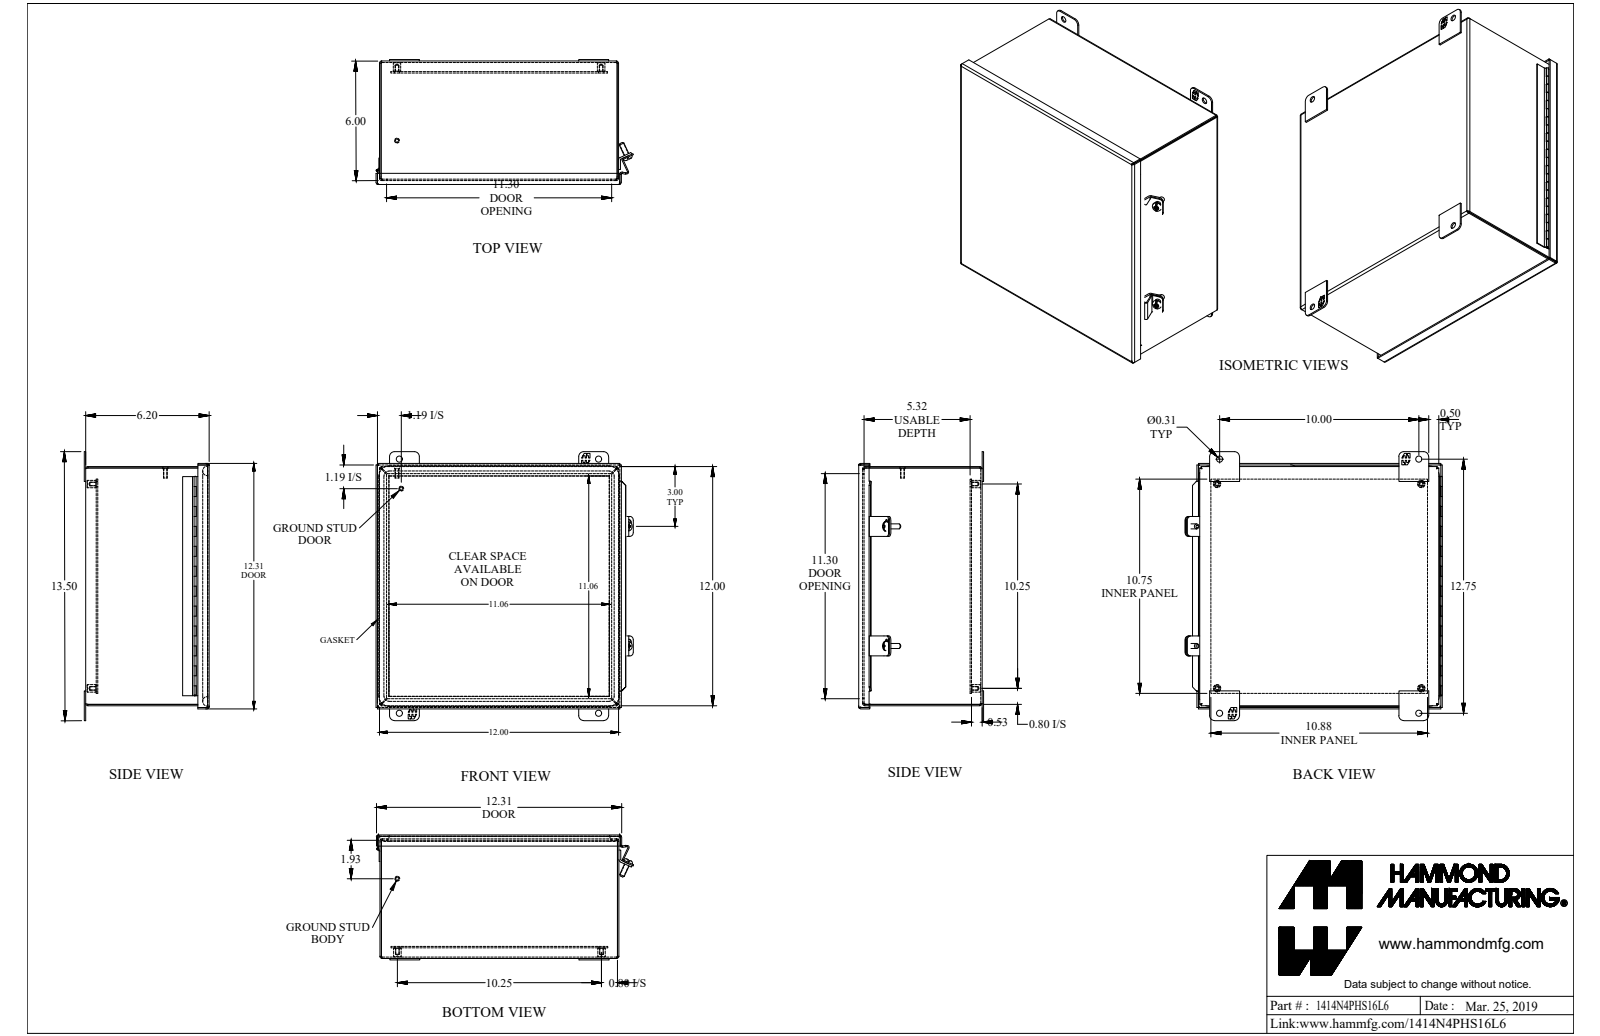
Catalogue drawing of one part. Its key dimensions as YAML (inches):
part_name: "1414N4PHS16L6"
step_written_by: "SolidWorks 2018 (AUTOMOTIVE_DESIGN)"
units: inches
bodies: {solids: 21, faces: 705, planar: 459, cylindrical: 188, other: 58}
overall_size: [13.5, 12.903, 6.269]
volume: 60.37
surface_area: 1649
round_holes:
  - {diameter: 0.156, count: 4}
  - {diameter: 0.265, count: 4}
  - {diameter: 0.313, count: 4}
  - {diameter: 0.213, count: 2}
  - {diameter: 0.05, count: 1}
round_bosses_or_shafts:
  - {diameter: 0.375, count: 4}
  - {diameter: 0.25, count: 4}
  - {diameter: 0.48, count: 2}
  - {diameter: 0.19, count: 2}
  - {diameter: 0.1, count: 1}
  - {diameter: 0.045, count: 1}
partial_cylinders:
  - {radius: 0.25, count: 24}
  - {radius: 0.036, count: 8}
  - {radius: 0.108, count: 8}
  - {radius: 0.188, count: 8}
  - {radius: 0.079, count: 4}
  - {radius: 0.118, count: 4}
  - {radius: 0.141, count: 4}
  - {radius: 0.499, count: 4}
face_to_face_distances: [0.072, 11.928, 0.532, 0.081, 6.116, 6.197, 6.125, 6.044, 11.856, 12]
hole_center_spacings: [10.25, 10.25, 10.202, 1.256, 11.501, 14.496, 15.322, 1.256]
